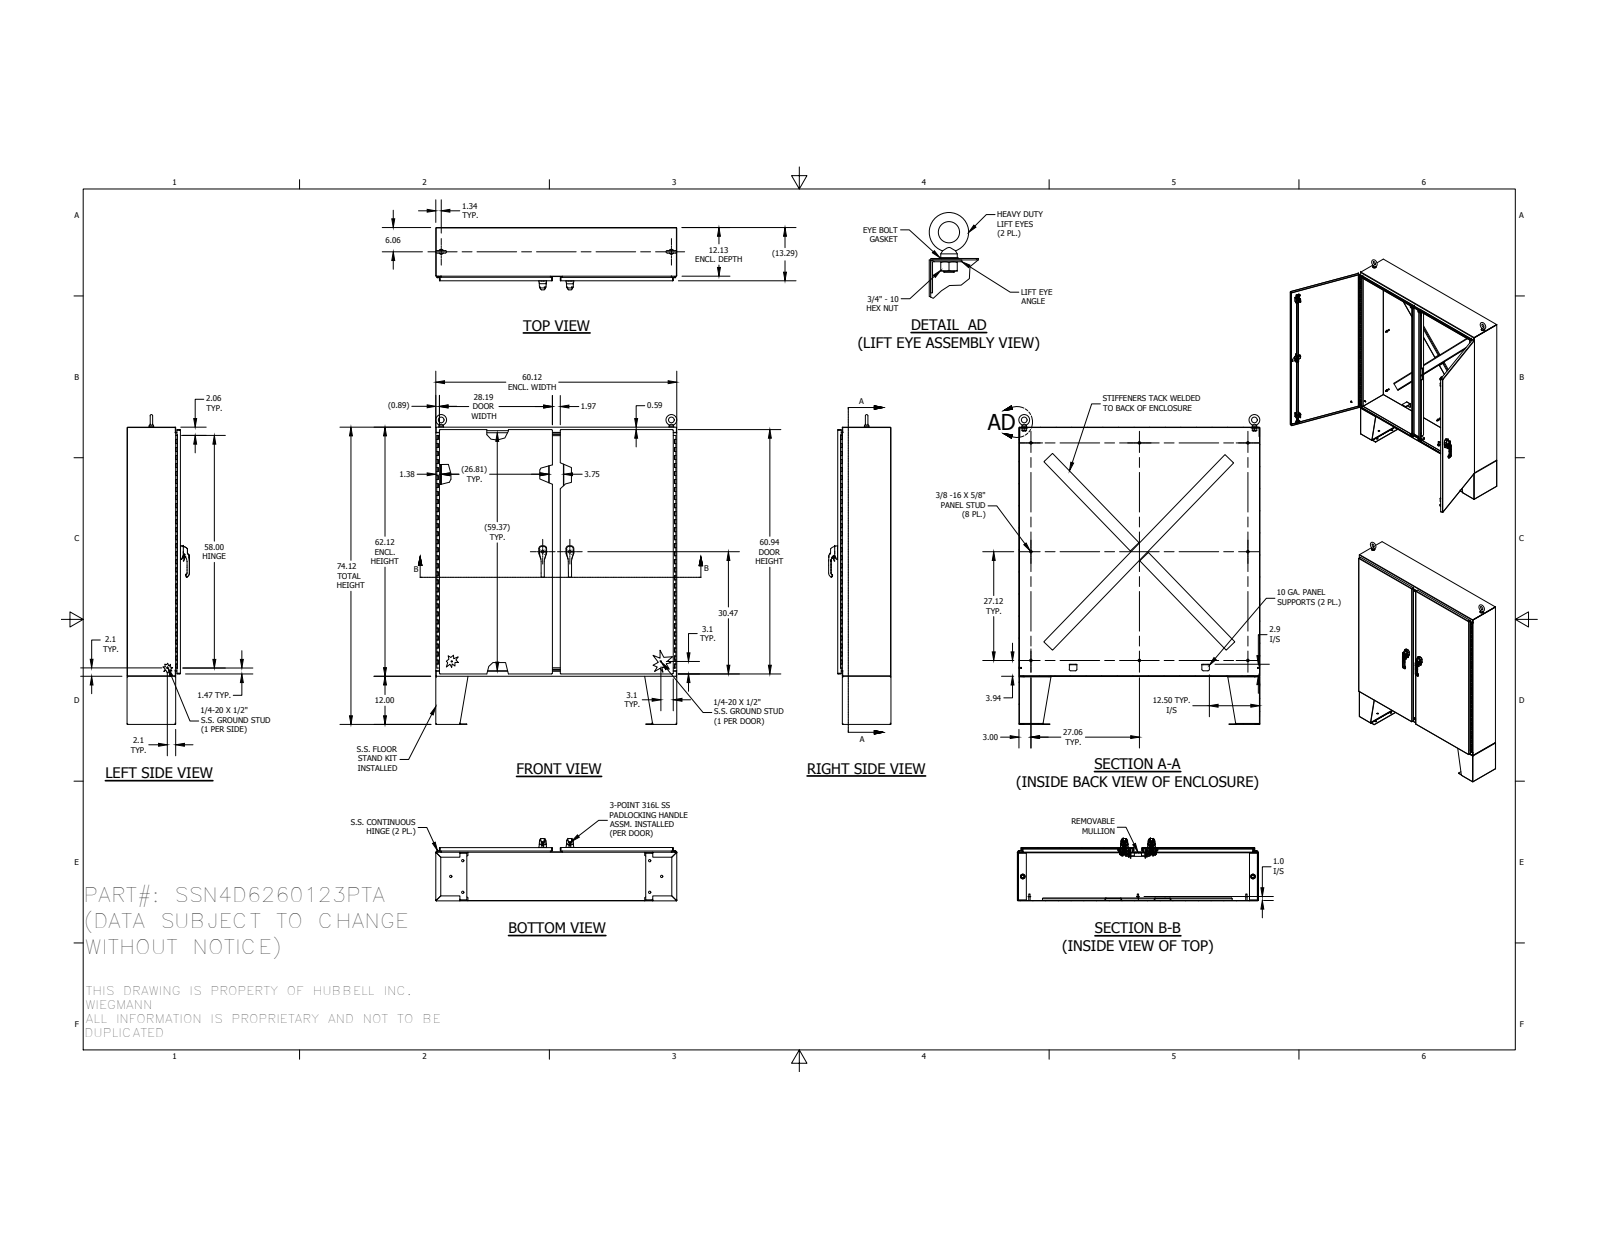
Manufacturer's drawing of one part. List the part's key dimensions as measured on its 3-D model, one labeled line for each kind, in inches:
Part name (STEP PRODUCT): 328131-58_1; 328131-58_1_1; SSFK1212_1; HFW32451_1 (+8 more)
STEP written by: SolidWorks 2014 (AUTOMOTIVE_DESIGN)
Units: inches
Bodies: 138 solids, 7184 faces (2696 planar, 2772 cylindrical, 1716 other)
Overall size (bounding box): 77.248 × 60.125 × 15.538
Volume: 1 333 in³ · Surface area: 27 833 in²
Round holes (diameter × count): ⌀0.563 ×18, ⌀0.262 ×16, ⌀0.375 ×16, ⌀0.187 ×8, ⌀0.213 ×6, ⌀0.281 ×6, ⌀0.25 ×5, ⌀0.196 ×4, ⌀0.241 ×4, ⌀0.252 ×4, ⌀0.281 ×4, ⌀0.315 ×4
Round bosses / shafts (diameter × count): ⌀0.33 ×10, ⌀0.625 ×8, ⌀0.25 ×7, ⌀0.533 ×6, ⌀0.236 ×6, ⌀1 ×5, ⌀0.563 ×4, ⌀0.531 ×4
Partial cylindrical surfaces — rounded edges, fillets, slot ends (radius × count): R0.02 ×350, R0.012 ×213, R0.125 ×46, R0.019 ×44, R0.05 ×34, R0.031 ×32, R0.079 ×28, R0.025 ×24
Main face-to-face distances: 0.094, 13.196, 13.193, 13.102, 13.1, 13.29, 0.096, 13.287, 0.091, 60.031
Hole centre spacings: 6.444, 0.38, 0.38, 0.76, 12.889, 52.052, 52.427, 52.802
